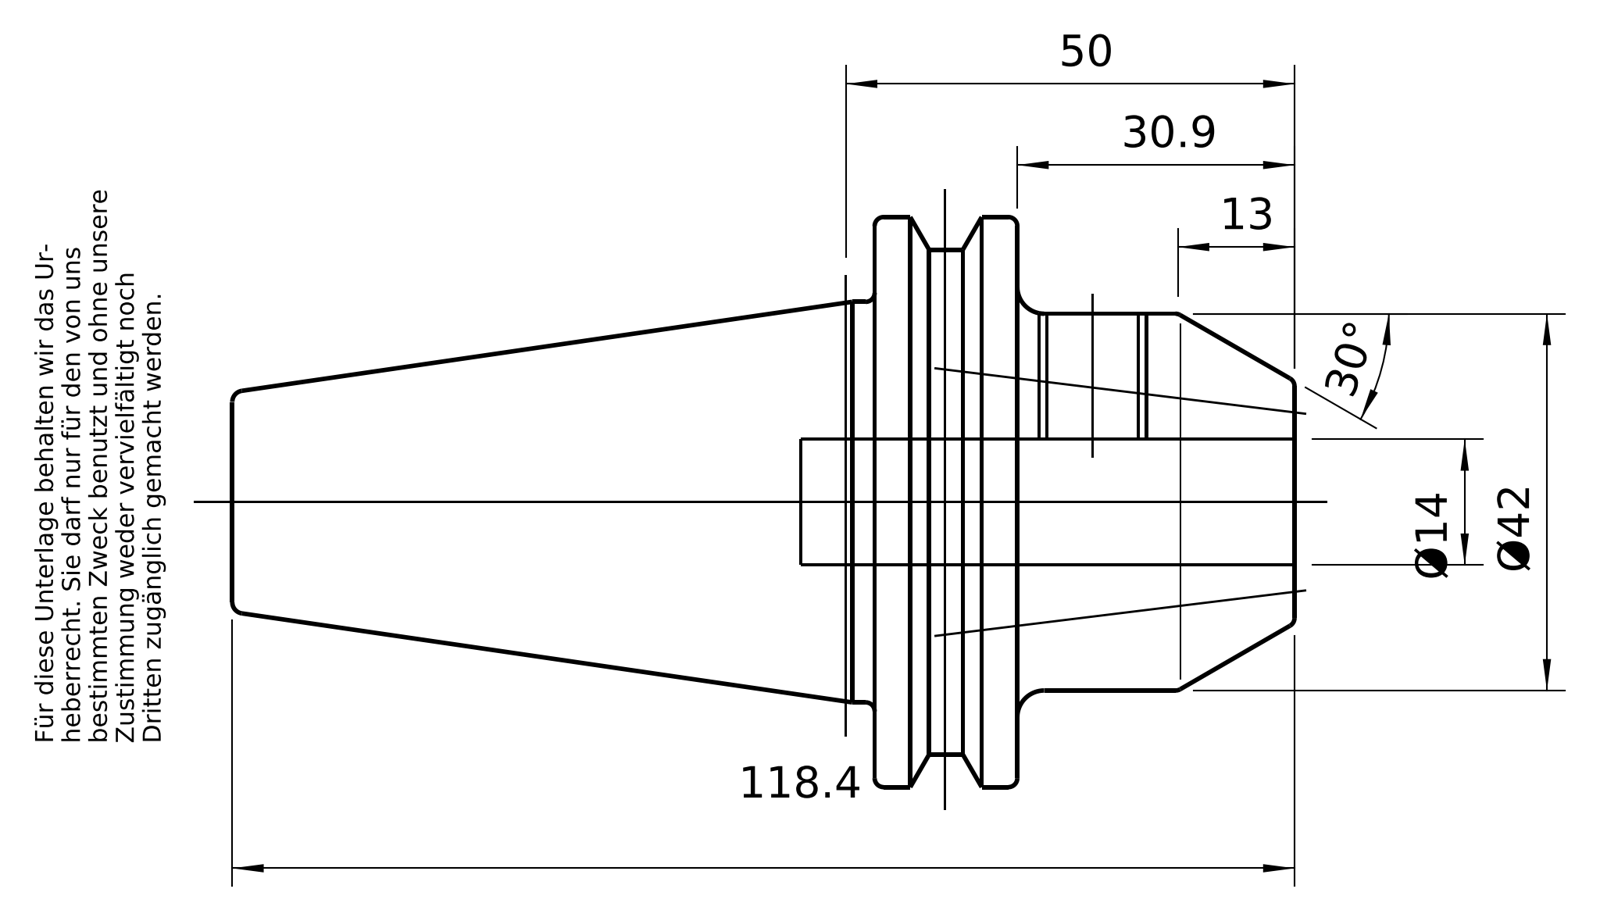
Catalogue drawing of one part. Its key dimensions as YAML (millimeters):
part_name: "40-300-14"
step_written_by: "PRO/ENGINEER BY PARAMETRIC TECHNOLOGY CORPORATION, 2010430 (CONFIG_CONTROL_DESIGN)"
units: millimeters
bodies: {solids: 1, faces: 99, planar: 21, cylindrical: 28, other: 50}
overall_size: [118.25, 63.52, 61.42]
volume: 133319
surface_area: 26372
round_holes:
  - {diameter: 10.2, count: 1}
  - {diameter: 12, count: 1}
  - {diameter: 13.84, count: 1}
  - {diameter: 14, count: 1}
  - {diameter: 17.01, count: 1}
  - {diameter: 17.5, count: 1}
round_bosses_or_shafts:
  - {diameter: 43.75, count: 1}
  - {diameter: 42, count: 1}
  - {diameter: 16.01, count: 1}
partial_cylinders:
  - {radius: 1.35, count: 1}
  - {radius: 28, count: 1}
  - {radius: 31.76, count: 1}
face_to_face_distances: [15.85, 46.8, 30.95, 47.4, 16.2, 8.2, 24.05, 55, 63.25, 71.45]
